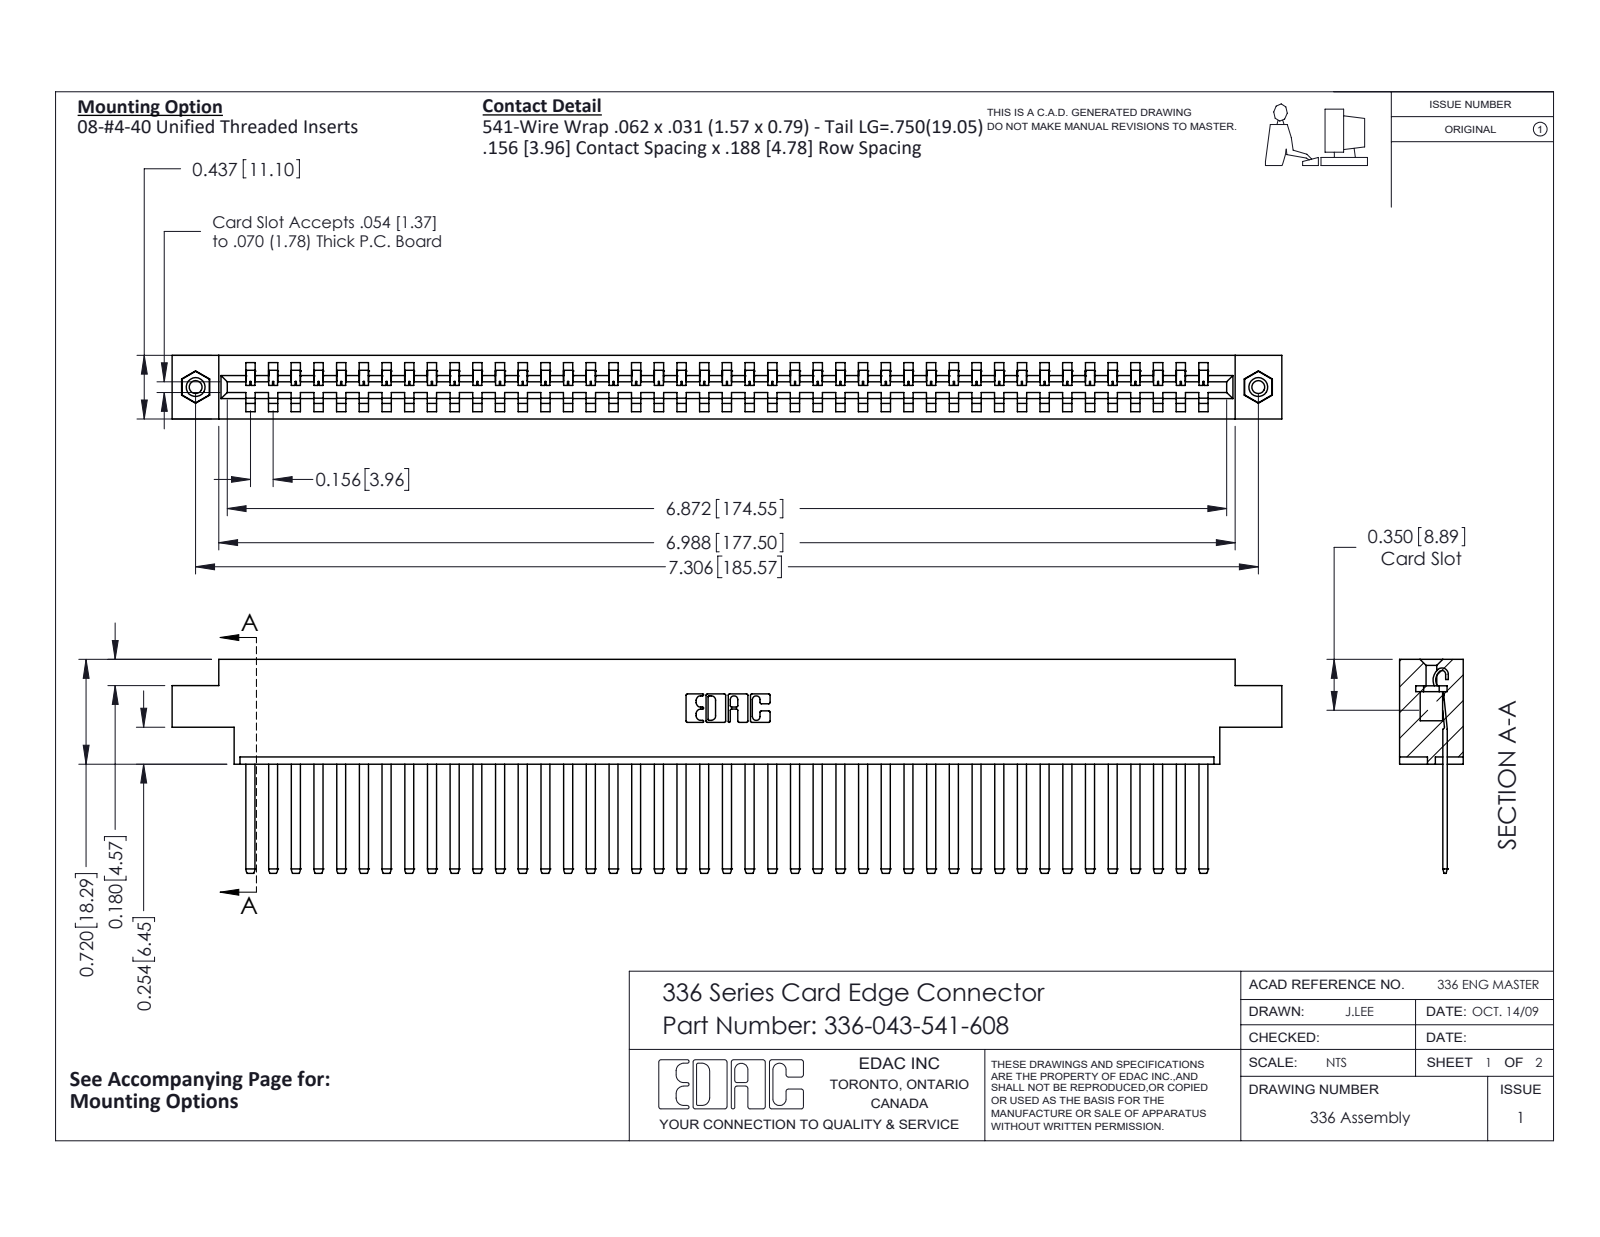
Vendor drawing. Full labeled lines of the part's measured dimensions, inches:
Part name (STEP PRODUCT): 336-043-541-608; 336-290-001_336-290-541; 336 Part_Offset - .156 Dia - TI; 345-250-001_345-250-003-102
STEP written by: SolidWorks 2020 (CONFIG_CONTROL_DESIGN)
Units: inches
Bodies: 46 solids, 2328 faces (1568 planar, 744 cylindrical, 16 other)
Overall size (bounding box): 7.629 × 1.47 × 0.437
Volume: 1.724 in³ · Surface area: 47.86 in²
Round holes (diameter × count): ⌀0.089 ×2, ⌀0.125 ×2, ⌀0.156 ×2
Round bosses / shafts (diameter × count): ⌀0.155 ×2
Partial cylindrical surfaces — rounded edges, fillets, slot ends (radius × count): R0.004 ×86, R0.056 ×86, R0.01 ×22, R0.007 ×6, R0.031 ×6, R0.026 ×3, R0.022 ×2, R0.04 ×2
Main face-to-face distances: 0.437, 0.181, 0.328, 0.14, 0.297, 0.109, 0.031, 0.256, 0.05, 0.131
Hole centre spacings: 7.306
